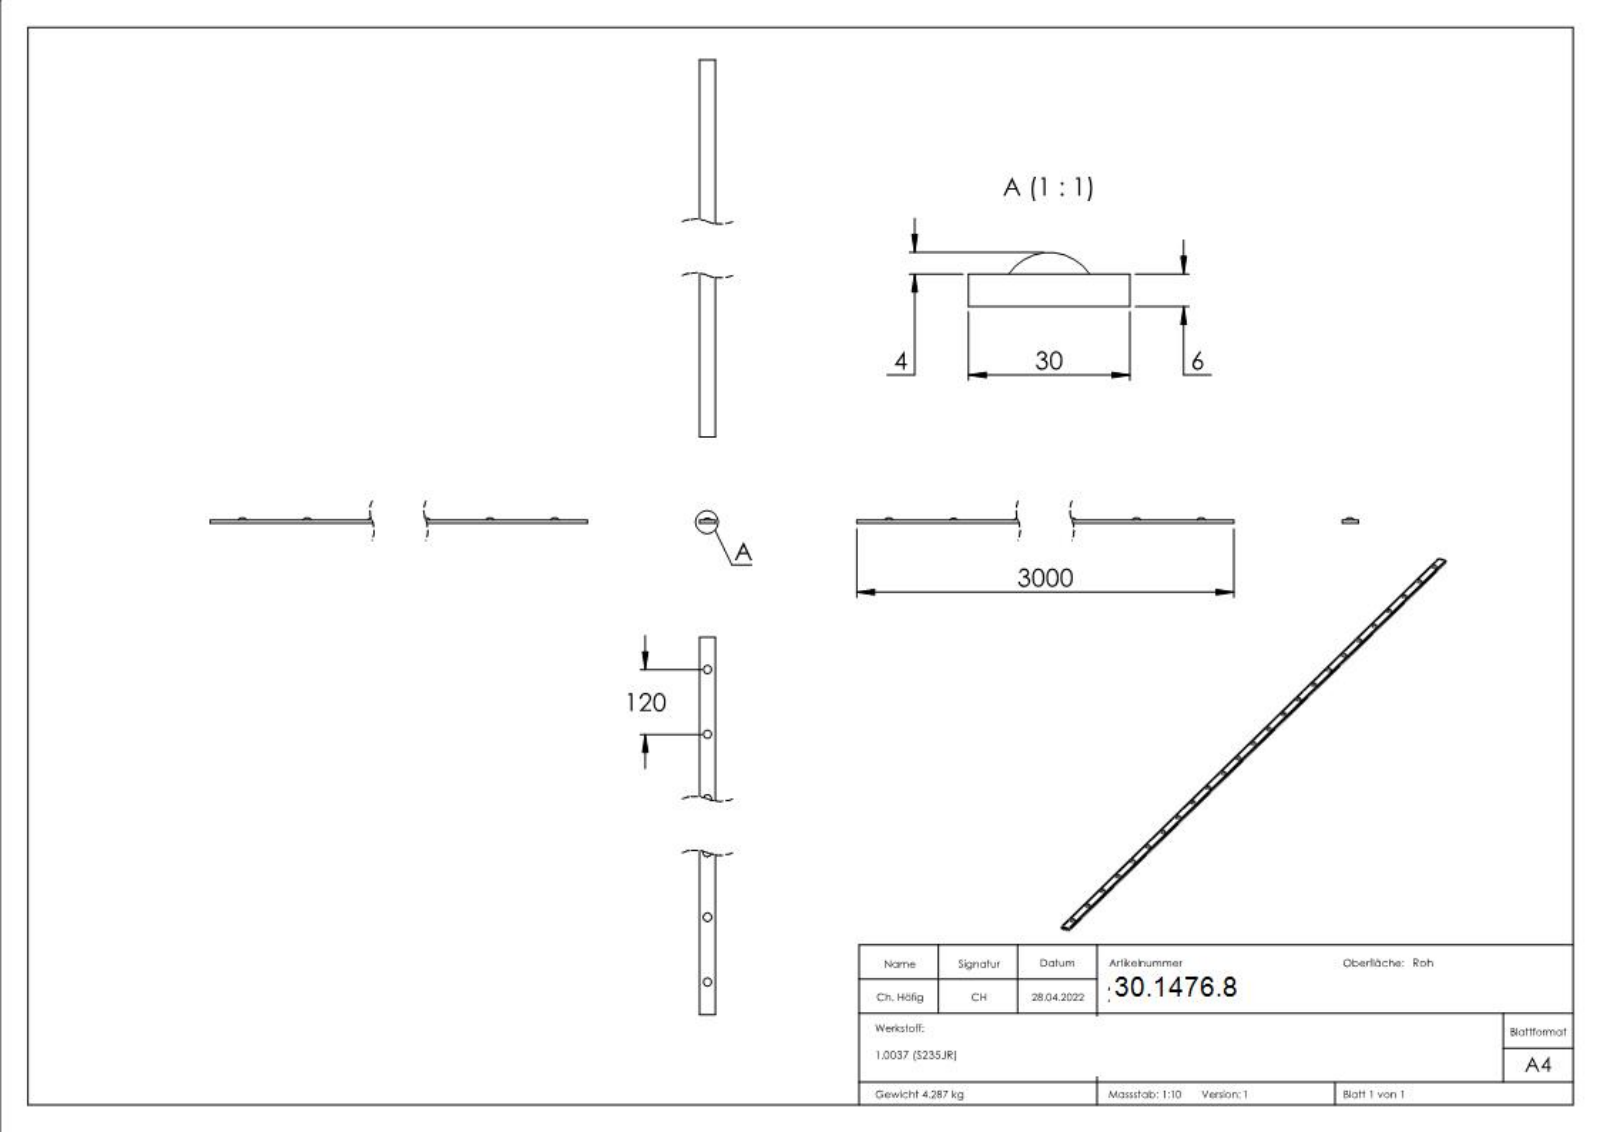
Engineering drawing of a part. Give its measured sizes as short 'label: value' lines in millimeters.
name: 2305-N
written by: SolidWorks 2018 (CONFIG_CONTROL_DESIGN)
unit: mm
bodies: 1 solid, 260 faces (130 planar, 0 cylindrical, 130 other)
size: 3000 × 30 × 10
volume: 549 671 mm³; area: 217 627 mm²
face distances: 6, 30, 3000, 5.9, 0.9, 2.84, 3.98, 3.27, 0.88, 3.2
